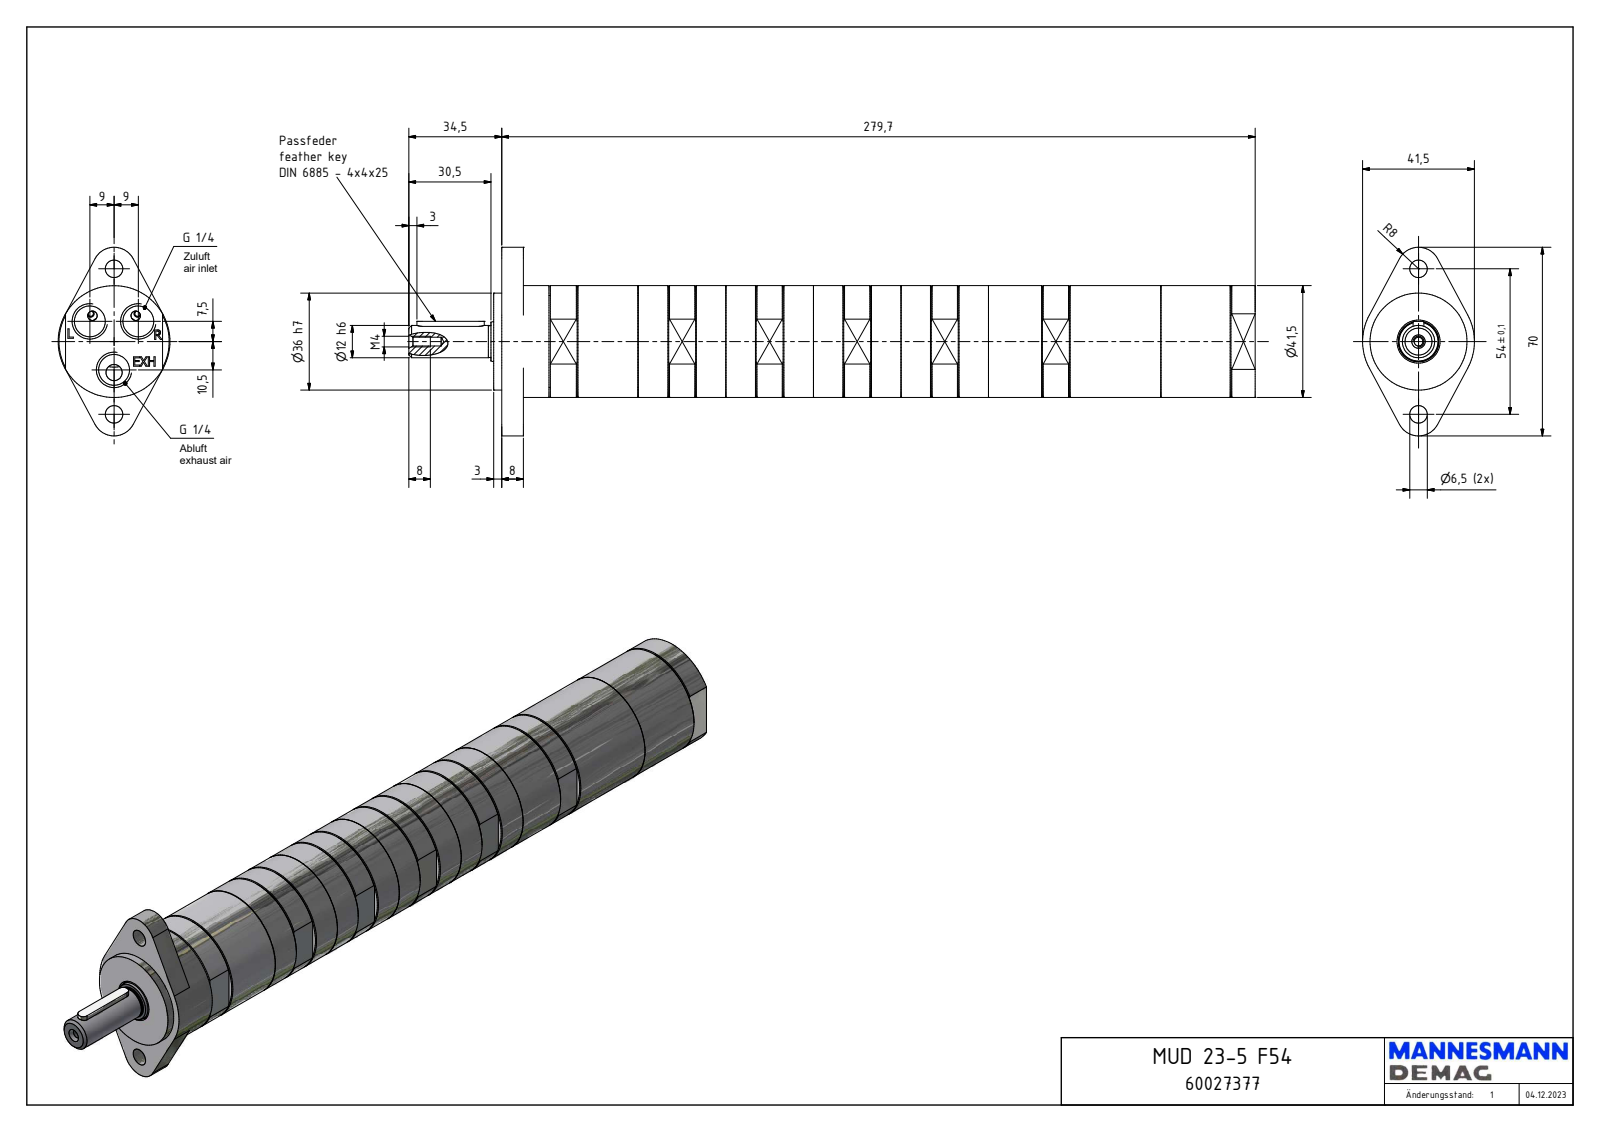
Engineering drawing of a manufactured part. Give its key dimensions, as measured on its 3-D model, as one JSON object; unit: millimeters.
{"part_name": "MUD 23-5 F54_60027377", "step_written_by": "Autodesk Inventor 2024 (AUTOMOTIVE_DESIGN)", "units": "millimeters", "bodies": {"solids": 1, "faces": 216, "planar": 119, "cylindrical": 44, "other": 53}, "overall_size": [314.2, 70, 41.5], "volume_mm3": 382654, "surface_area_mm2": 45059, "round_holes": [[11.45, 3], [6.5, 2], [3.24, 1], [16, 1]], "round_bosses_or_shafts": [[41.5, 1], [37.99, 1], [36, 1], [14.95, 1], [12, 1], [11.8, 1]], "partial_cylinders_radius": [[2, 2], [8, 2]], "face_to_face_distances": [38, 279.7, 3, 282.7, 10, 11, 8, 271.7, 261.7, 1], "hole_center_spacings": [11.72, 20.12, 21.48, 27, 35.65, 10.5, 16.5, 18]}
